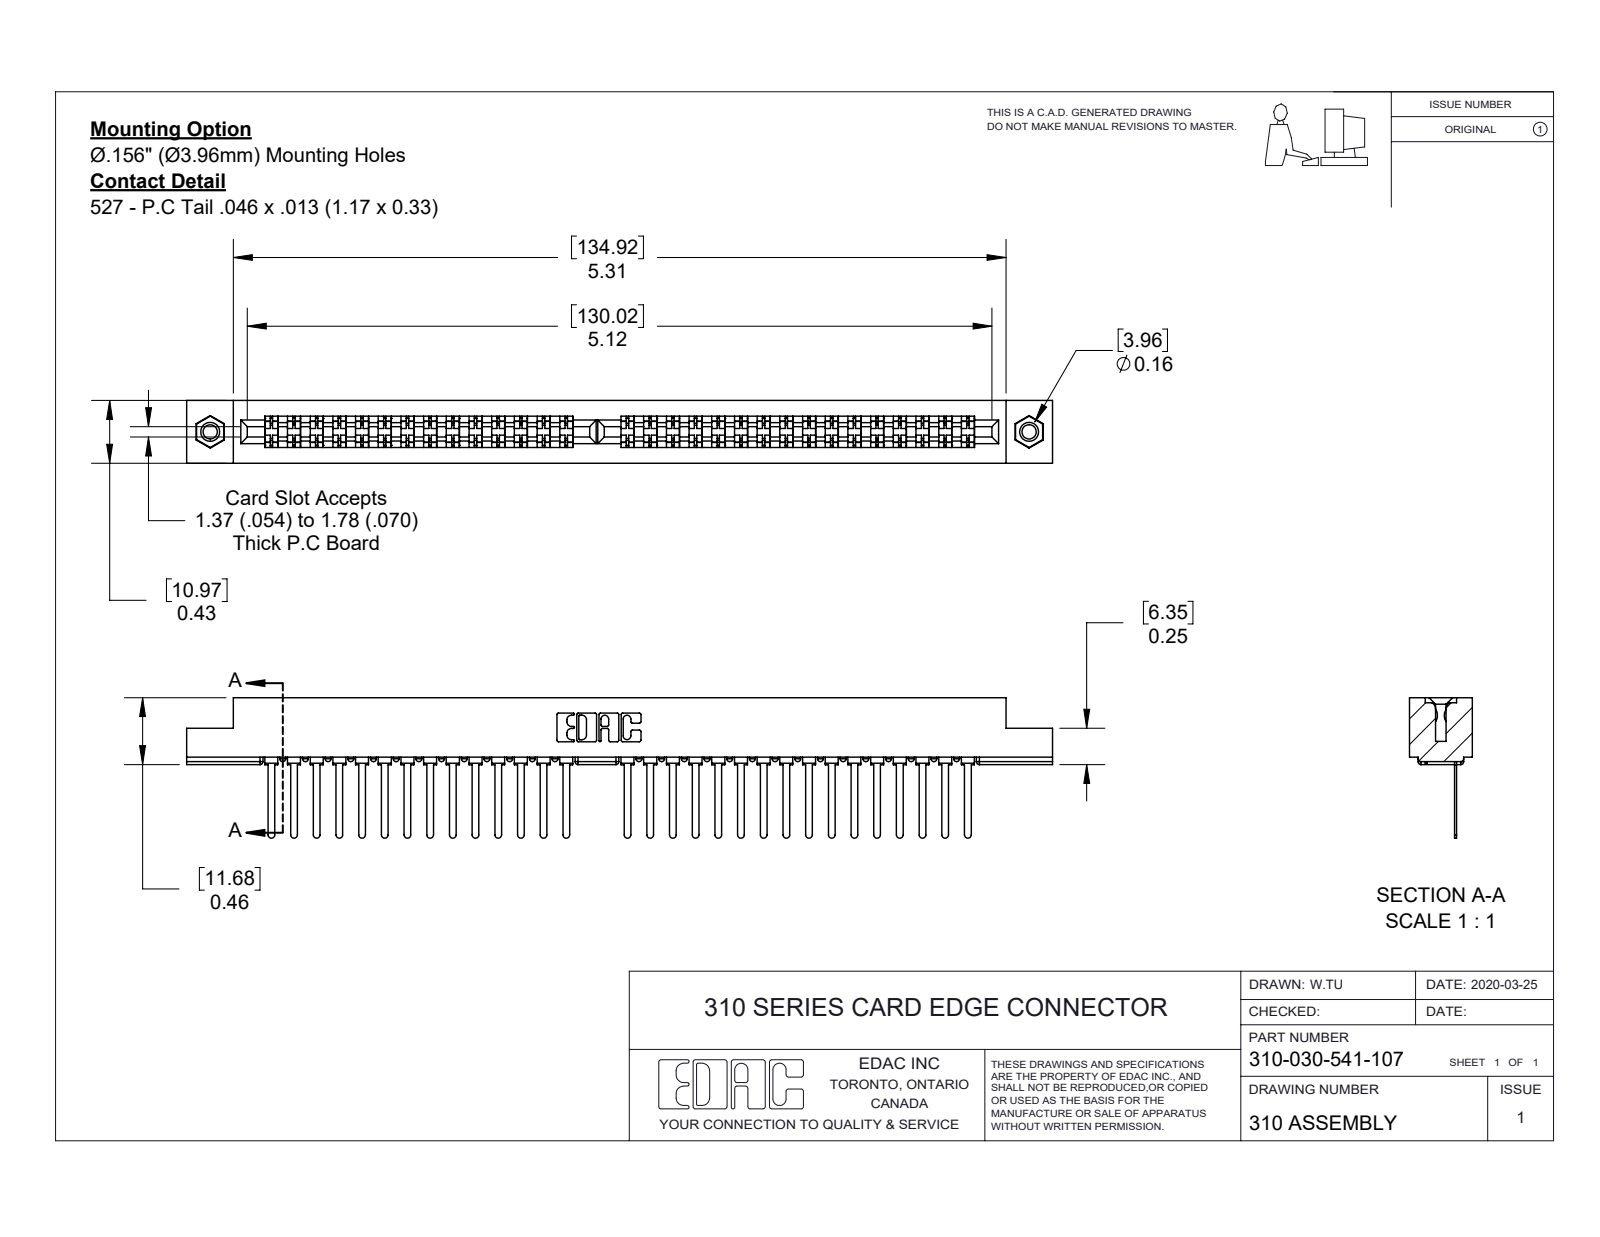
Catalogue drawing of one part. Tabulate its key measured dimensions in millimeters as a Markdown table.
| quantity | value |
| --- | --- |
| part name | 310-030-541-107; 307-290-002_541; 310 Part_.116 Hex; 345-250-001_345-250-005-103 |
| STEP written by | SolidWorks 2016 (CONFIG_CONTROL_DESIGN) |
| units | millimeters |
| bodies | 33 solids, 2446 faces (1466 planar, 900 cylindrical, 80 other) |
| overall size | 151.21 × 24.54 × 10.97 |
| volume | 13 173 mm³ |
| surface area | 19 047 mm² |
| round holes (diameter × count) | 2.5 × 2, 3.17 × 2, 3.96 × 2 |
| round bosses / shafts (diameter × count) | 3.94 × 2 |
| partial cylindrical surfaces (radius × count) | 0.51 × 98, 0.58 × 30, 0.25 × 22, 0.17 × 6, 0.8 × 6, 0.67 × 3, 0.31 × 2, 0.64 × 2 |
| main face-to-face distances | 2.76, 8.22, 0.33, 5.13, 3.09, 7.89, 10.98, 5.46, 1.24, 3.89 |
| hole center spacings | 143 |
